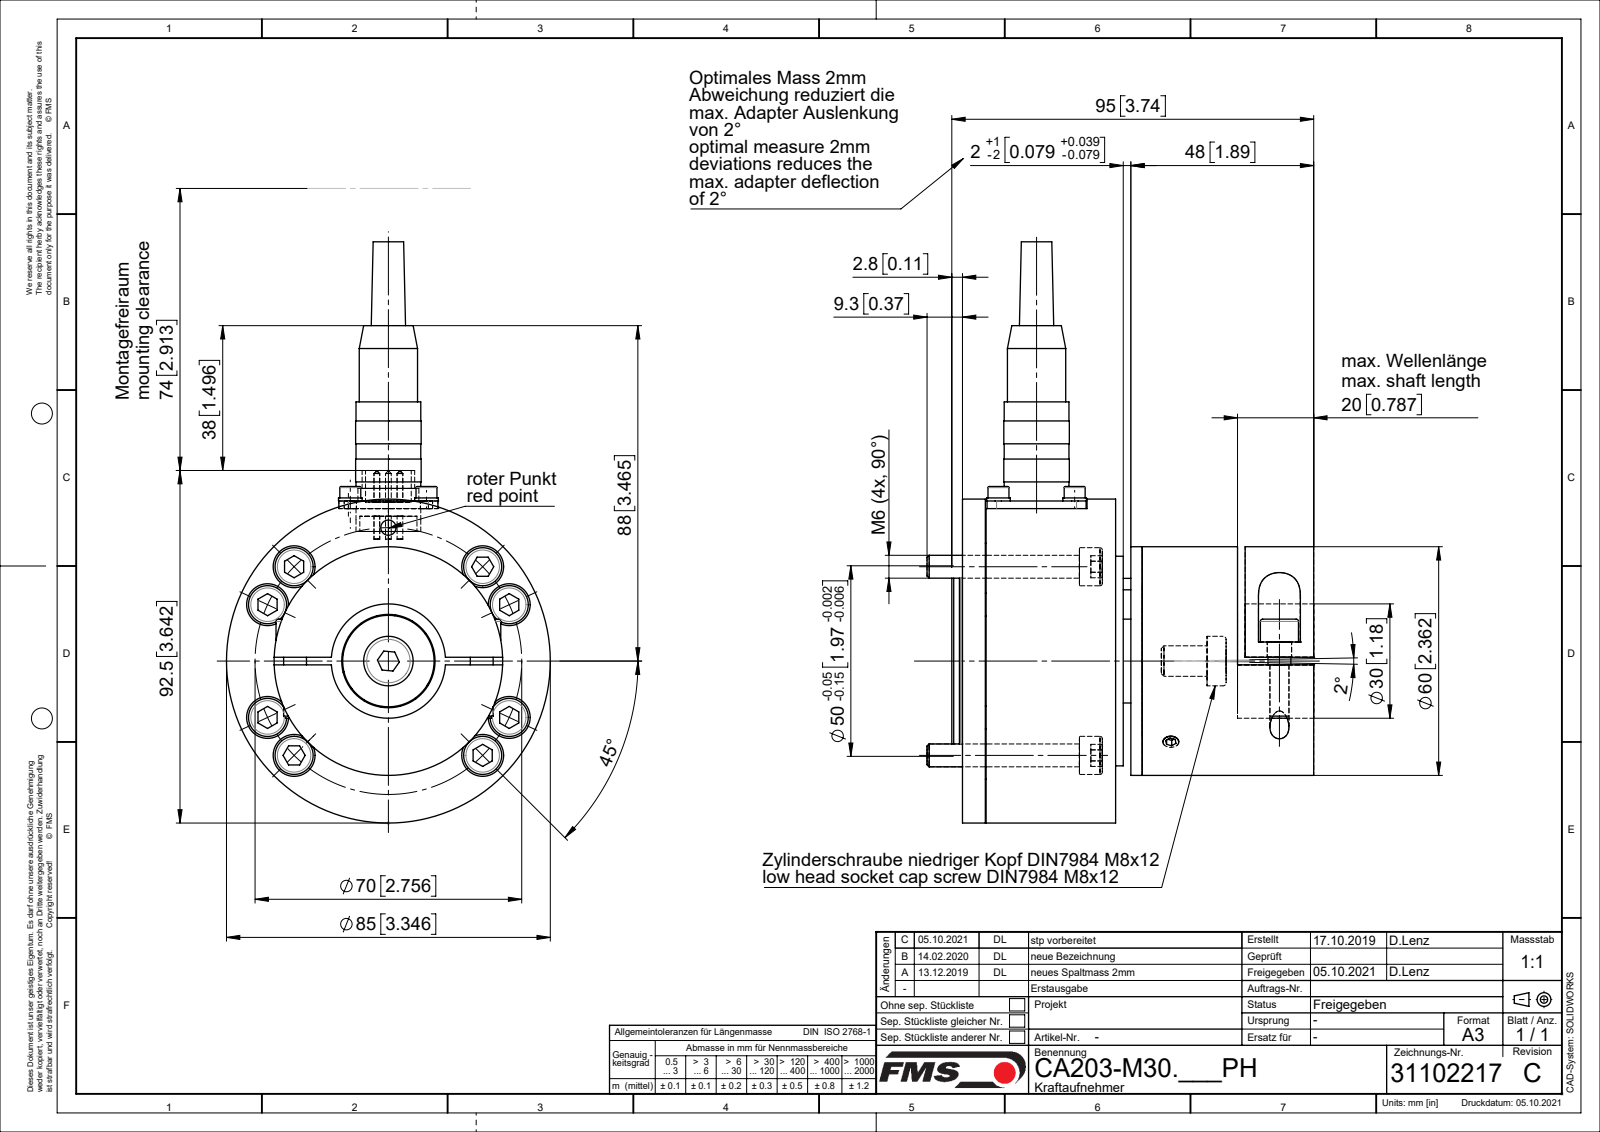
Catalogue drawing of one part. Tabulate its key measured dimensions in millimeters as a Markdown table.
| quantity | value |
| --- | --- |
| part name | Se-Schr DIN7991_M3x8; 070907-2_01; Senkniete_90°_d3x10; RKL_6203_01 (+8 more) |
| STEP written by | SolidWorks 2018 (CONFIG_CONTROL_DESIGN) |
| units | millimeters |
| bodies | 44 solids, 821 faces (294 planar, 332 cylindrical, 195 other) |
| overall size | 152.5 × 101.5 × 85 |
| volume | 298 525 mm³ |
| surface area | 109 729 mm² |
| round holes (diameter × count) | 2.5 × 8, 6.5 × 8, 11 × 8, 5 × 6, 4 × 5, 3.1 × 4, 3.2 × 4, 3.6 × 4, 7 × 4, 6.4 × 2, 3 × 1, 4.2 × 1 |
| round bosses / shafts (diameter × count) | 6 × 11, 10 × 10, 3 × 8, 1.5 × 5, 6.2 × 4, 5.7 × 4, 5.5 × 4, 85 × 1 |
| partial cylindrical surfaces (radius × count) | 2.5 × 4, 5 × 2, 5.5 × 2 |
| main face-to-face distances | 2, 41, 30, 6, 45, 10, 50, 3, 34, 12 |
| hole center spacings | 35, 20, 24.78, 25.2, 32.8, 51.14, 56.46, 28.28 |
